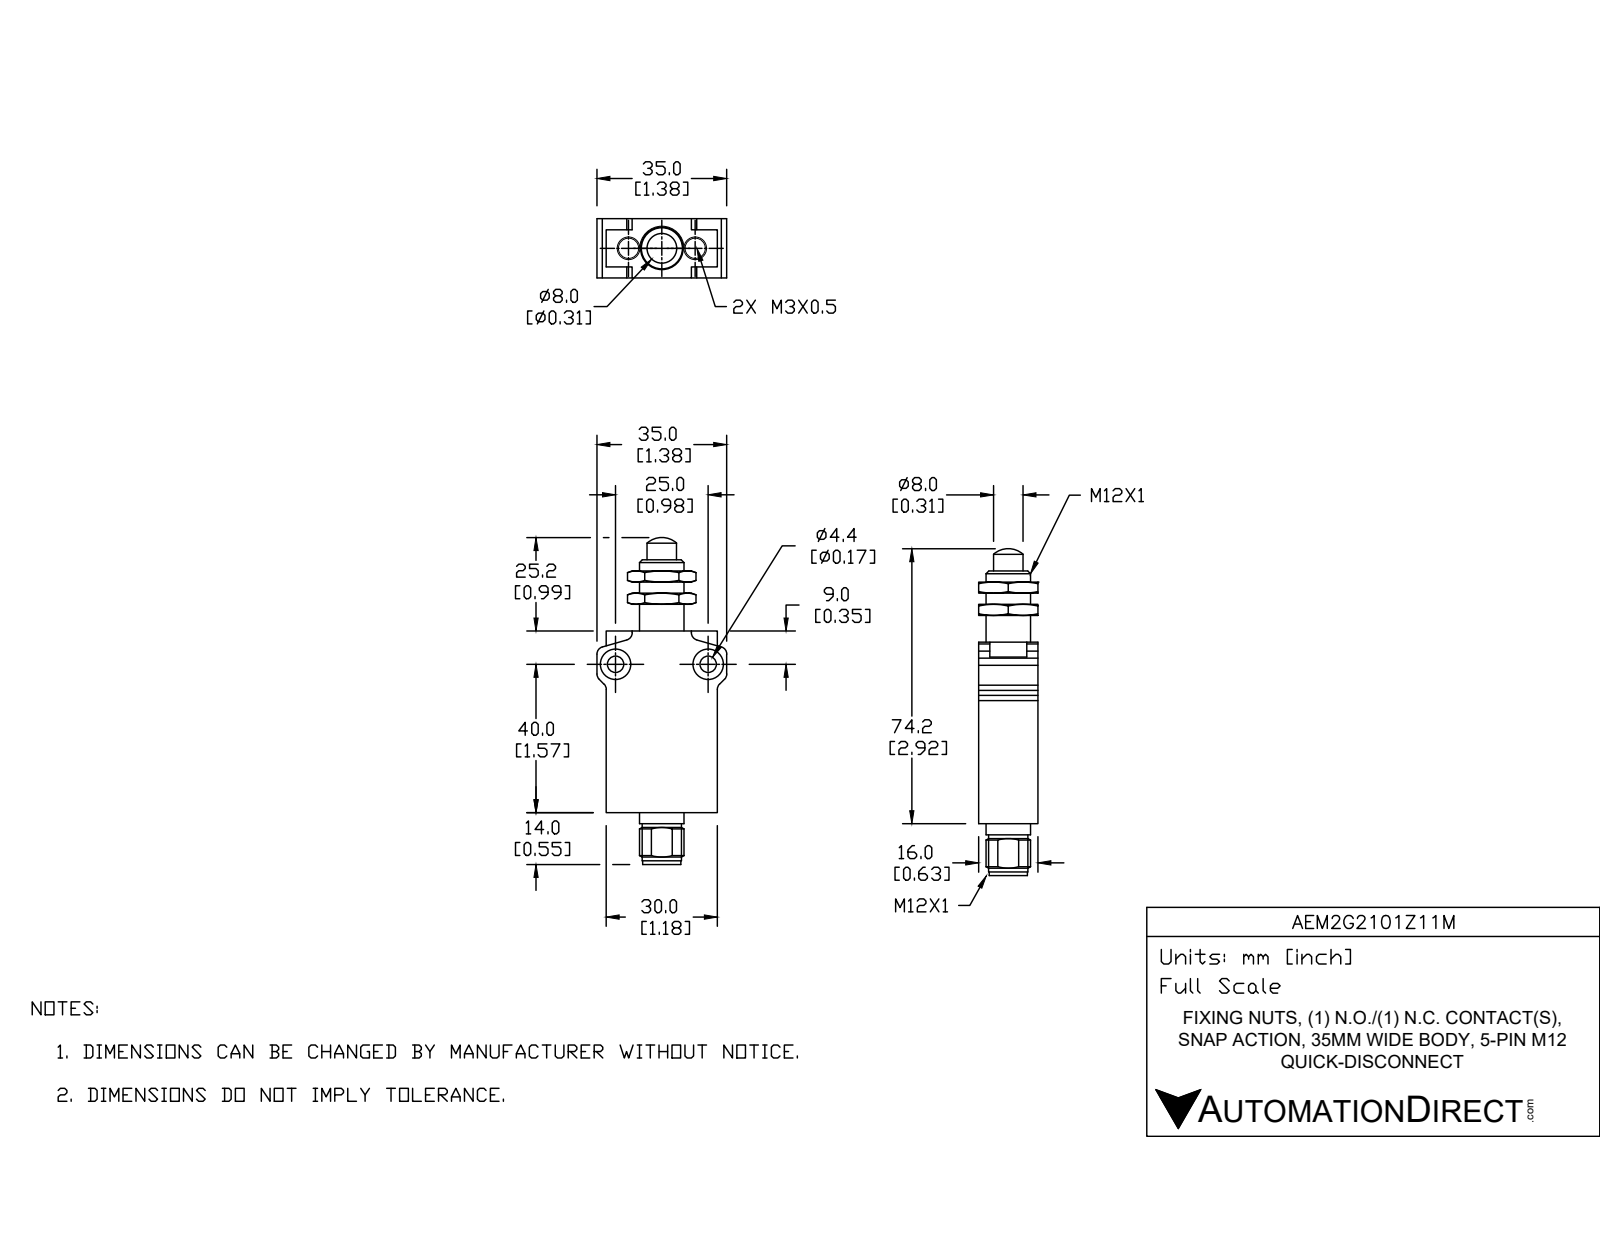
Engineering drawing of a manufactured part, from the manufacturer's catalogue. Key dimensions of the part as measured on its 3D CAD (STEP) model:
Part name (STEP PRODUCT): AEM2G2101Z11M
STEP written by: SolidWorks 2017 (AUTOMOTIVE_DESIGN)
Units: inches
Bodies: 5 solids, 198 faces (66 planar, 68 cylindrical, 64 other)
Overall size (bounding box): 3.589 × 1.378 × 0.682
Volume: 1.74 in³ · Surface area: 16.51 in²
Round holes (diameter × count): ⌀0.118 ×2, ⌀0.173 ×2, ⌀0.323 ×2, ⌀0.317 ×1
Round bosses / shafts (diameter × count): ⌀0.472 ×1, ⌀0.417 ×1, ⌀0.406 ×1, ⌀0.313 ×1
Partial cylindrical surfaces — rounded edges, fillets, slot ends (radius × count): R0.079 ×8, R0.256 ×1
Main face-to-face distances: 0.63, 1.181, 0.472, 0.118, 0.236, 2.047, 0.354, 1.858, 0.189, 0.098
Hole centre spacings: 0.374, 0.748, 0.984
